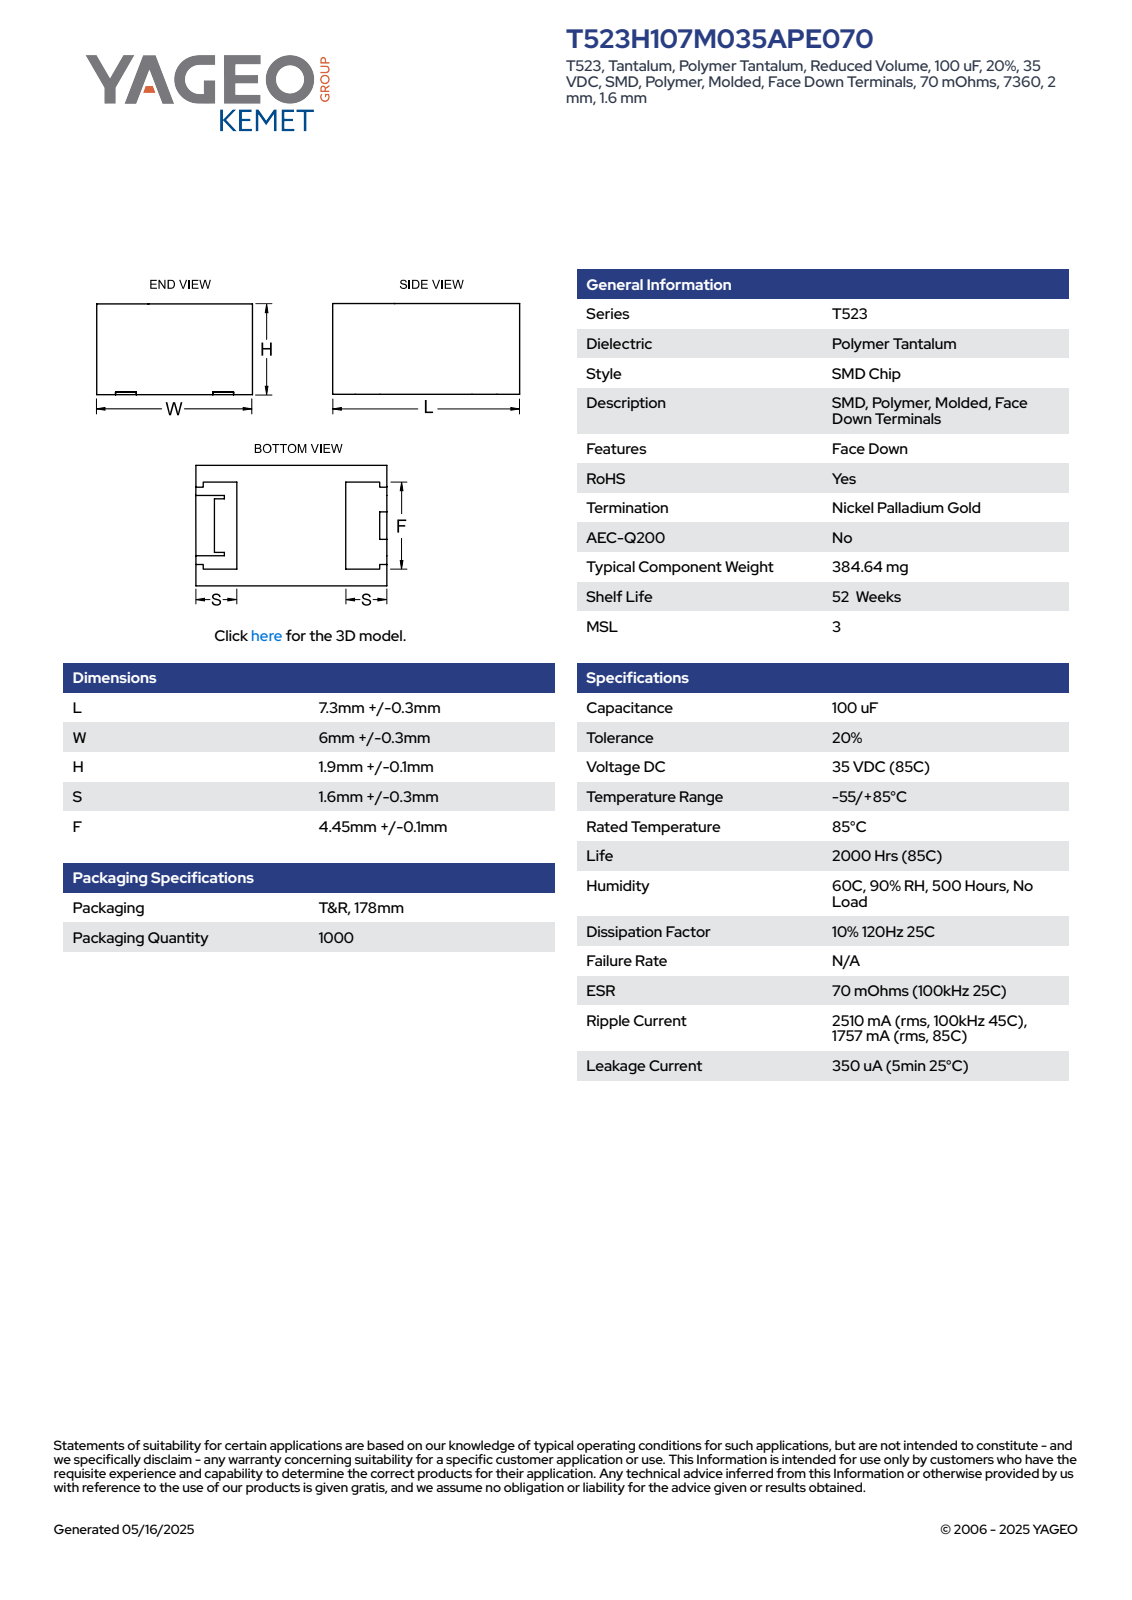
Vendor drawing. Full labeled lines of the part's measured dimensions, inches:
Part name (STEP PRODUCT): CTS_TFD_H_7360_L7.6W6.3H2S1.6F4.55
STEP written by: SolidWorks 2020 (AUTOMOTIVE_DESIGN)
Units: inches
Bodies: 4 solids, 101 faces (101 planar, 0 cylindrical, 0 other)
Overall size (bounding box): 0.3 × 0.248 × 0.079
Volume: 0.006 in³ · Surface area: 0.245 in²
Main face-to-face distances: 0.079, 0.248, 0.299, 0.079, 0.3, 0.3, 0.063, 0.237, 0.063, 0.236
